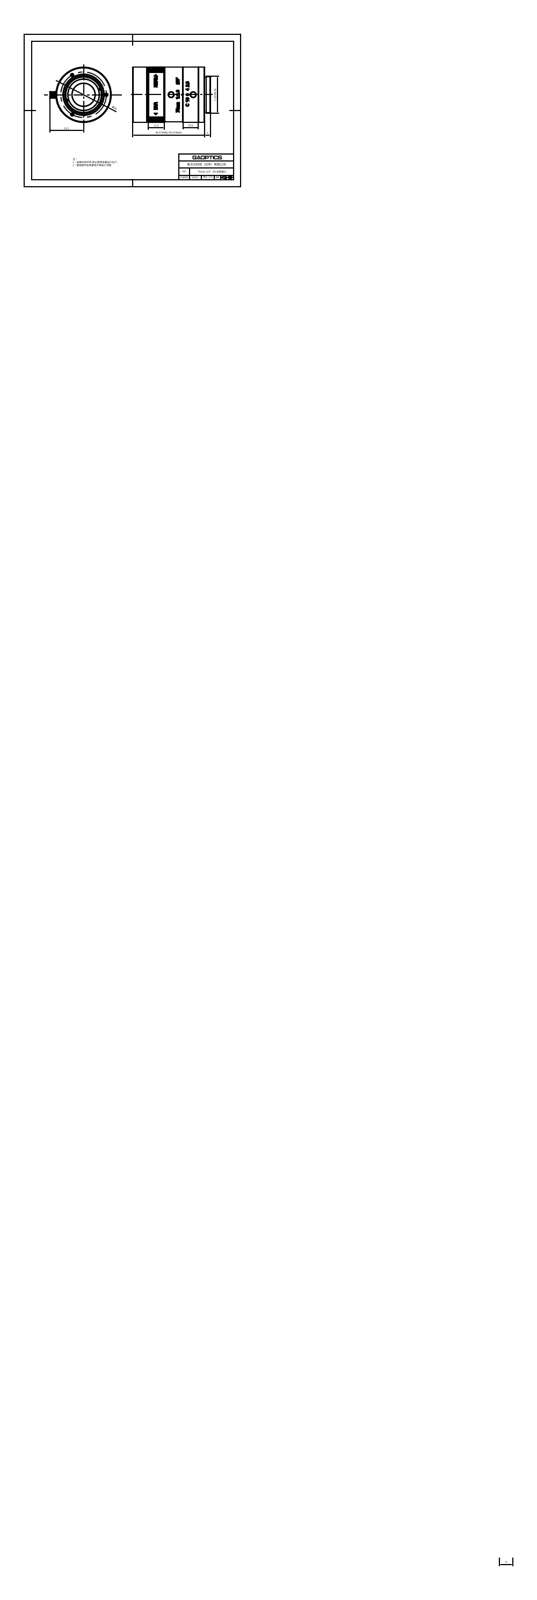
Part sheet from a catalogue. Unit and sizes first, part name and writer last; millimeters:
Units: millimetres
Overall size (bounding box): 53.49 × 42.01 × 38
Round holes (diameter × count): ⌀1.3 ×6, ⌀1.2 ×5, ⌀2 ×4, ⌀10.8 ×1, ⌀11.8 ×1, ⌀12.8 ×1, ⌀13.4 ×1, ⌀14.4 ×1, ⌀21.6 ×1, ⌀27.1 ×1, ⌀29 ×1, ⌀29.9 ×1
Round bosses / shafts (diameter × count): ⌀1 ×3, ⌀2 ×2, ⌀38 ×1, ⌀37.6 ×1, ⌀36.04 ×1, ⌀33 ×1, ⌀30.5 ×1, ⌀28.5 ×1
Partial cylindrical surfaces — rounded edges, fillets, slot ends (radius × count): R2 ×2, R0.6 ×1, R17 ×1, R18.1 ×1, R18.8 ×1, R18.9 ×1, R19.1 ×1, R19.12 ×1
Main face-to-face distances: 1, 2.37, 1.37, 1.12, 0.61, 0.76, 1.61, 3, 47, 47.76
Hole centre spacings: 15.7, 27.19, 27.2, 15.71
Volume: 52 433 mm³ · Surface area: 24 574 mm²
Bodies: 11 solids, 1328 faces (481 planar, 290 cylindrical, 557 other)
Part name (STEP PRODUCT): 600005
STEP written by: SolidWorks 2020 (CONFIG_CONTROL_DESIGN)
